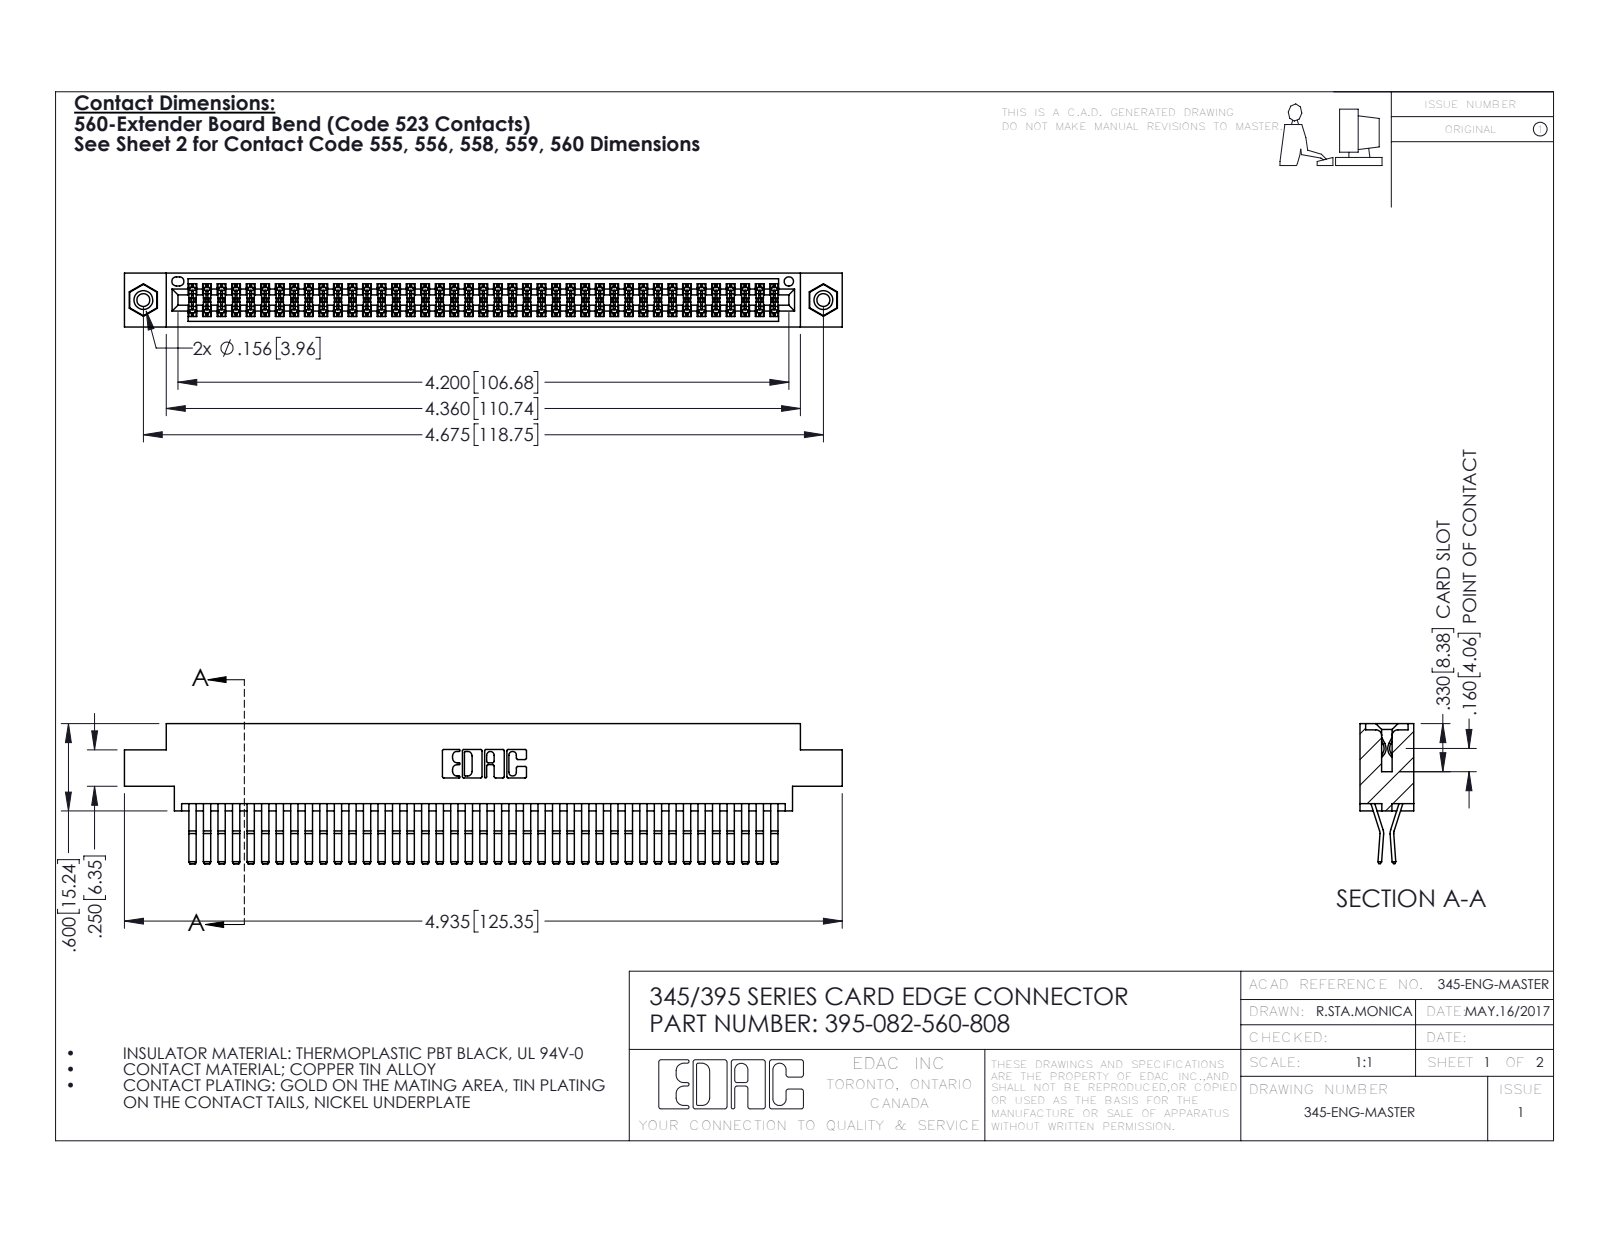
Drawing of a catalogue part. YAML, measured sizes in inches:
part_name: "345-292-001_560 Tail; 345-250-001_345-250-003-102; 345 Part_0.170 Offset - 0.156 Dia-TI; 395-082-560-808"
step_written_by: "SolidWorks 2016 (CONFIG_CONTROL_DESIGN)"
units: inches
bodies: {solids: 85, faces: 4454, planar: 2822, cylindrical: 1616, other: 16}
overall_size: [4.935, 0.962, 0.37]
volume: 0.768
surface_area: 31.19
round_holes:
  - {diameter: 0.089, count: 2}
  - {diameter: 0.125, count: 2}
  - {diameter: 0.156, count: 2}
  - {diameter: 0.064, count: 1}
round_bosses_or_shafts:
  - {diameter: 0.155, count: 2}
partial_cylinders:
  - {radius: 0.006, count: 124}
  - {radius: 0.01, count: 22}
  - {radius: 0.007, count: 6}
  - {radius: 0.031, count: 6}
  - {radius: 0.026, count: 3}
  - {radius: 0.01, count: 2}
  - {radius: 0.014, count: 2}
  - {radius: 0.019, count: 2}
face_to_face_distances: [0.025, 0.072, 0.298, 0.37, 0.2, 0.098, 0.272, 0.225, 0.175, 0.149]
hole_center_spacings: [0.27, 4.439, 4.675]
